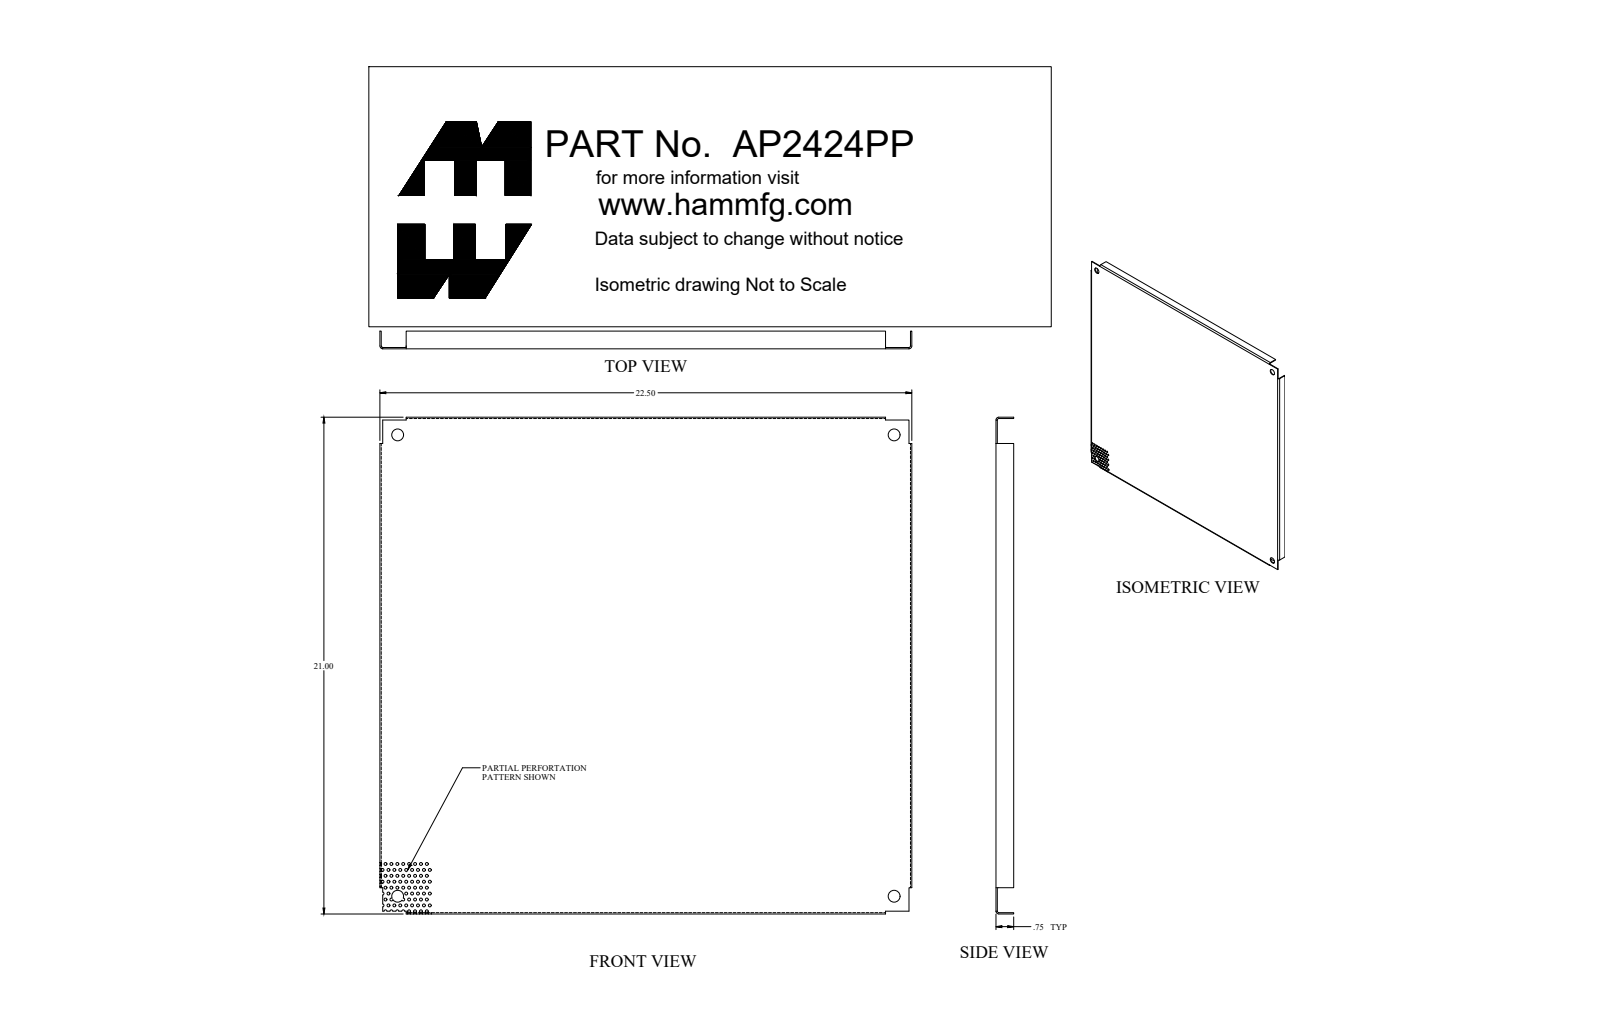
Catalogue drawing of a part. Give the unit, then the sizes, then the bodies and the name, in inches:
Units: inches
Overall size (bounding box): 22.5 × 21 × 0.75
Round holes (diameter × count): ⌀0.125 ×46, ⌀0.125 ×30, ⌀0.5 ×4
Partial cylindrical surfaces — rounded edges, fillets, slot ends (radius × count): R0.062 ×11, R0.063 ×10, R0.029 ×4, R0.086 ×4
Main face-to-face distances: 0.057, 20.943, 22.443, 21, 20.886, 22.386, 22.5, 0.75, 0.693, 0.102
Hole centre spacings: 0.28, 0.5, 0.25, 0.559, 0.451, 0.707, 0.75, 0.673
Volume: 29.73 in³ · Surface area: 1 051 in²
Bodies: 1 solid, 249 faces (43 planar, 198 cylindrical, 8 other)
Part name (STEP PRODUCT): AP2424PP_Default
STEP written by: SolidWorks 2019 (CONFIG_CONTROL_DESIGN)
